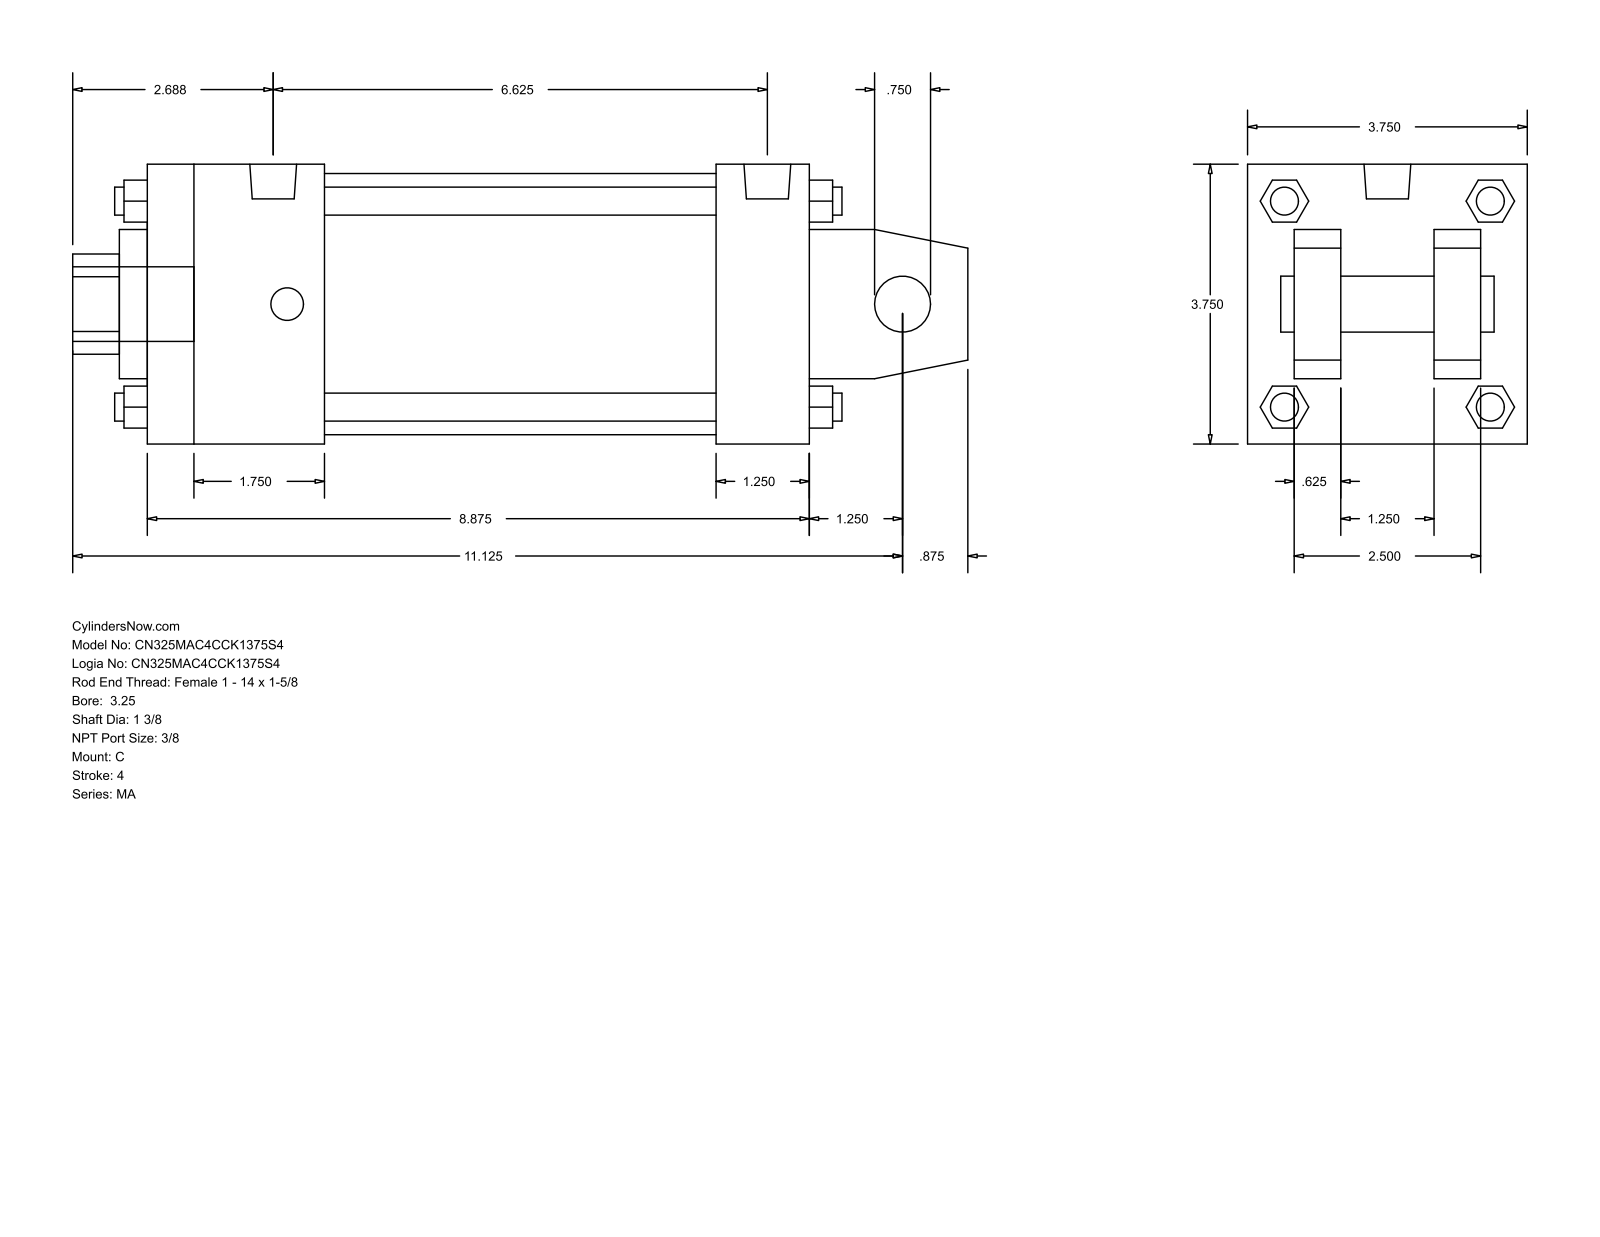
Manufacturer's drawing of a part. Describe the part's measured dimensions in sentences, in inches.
The part is named "MA_C__0325_1.375". Its 3-D file was written by "GSSL Pune (CONFIG_CONTROL_DESIGN)". It is 0 solids with 139 faces: 108 planar, 31 cylindrical and 0 other. Overall it measures 12 by 3.75 by 3.75 inches. Round holes: 1 of diameter 0.75, 1 of diameter 1.375, 1 of diameter 2, 1 of diameter 3.5. Round bosses or shafts: 4 of diameter 0.437, 4 of diameter 0.375, 2 of diameter 0.627, 1 of diameter 1. Partial cylindrical surfaces (rounded edges, fillets, slot ends): 1 of radius 0.672. The main face-to-face distances are 3.75, 0.625, 2.5, 8.875, 1.25, 3.125, 1.875, 7.625, 1.25, 2.375.
